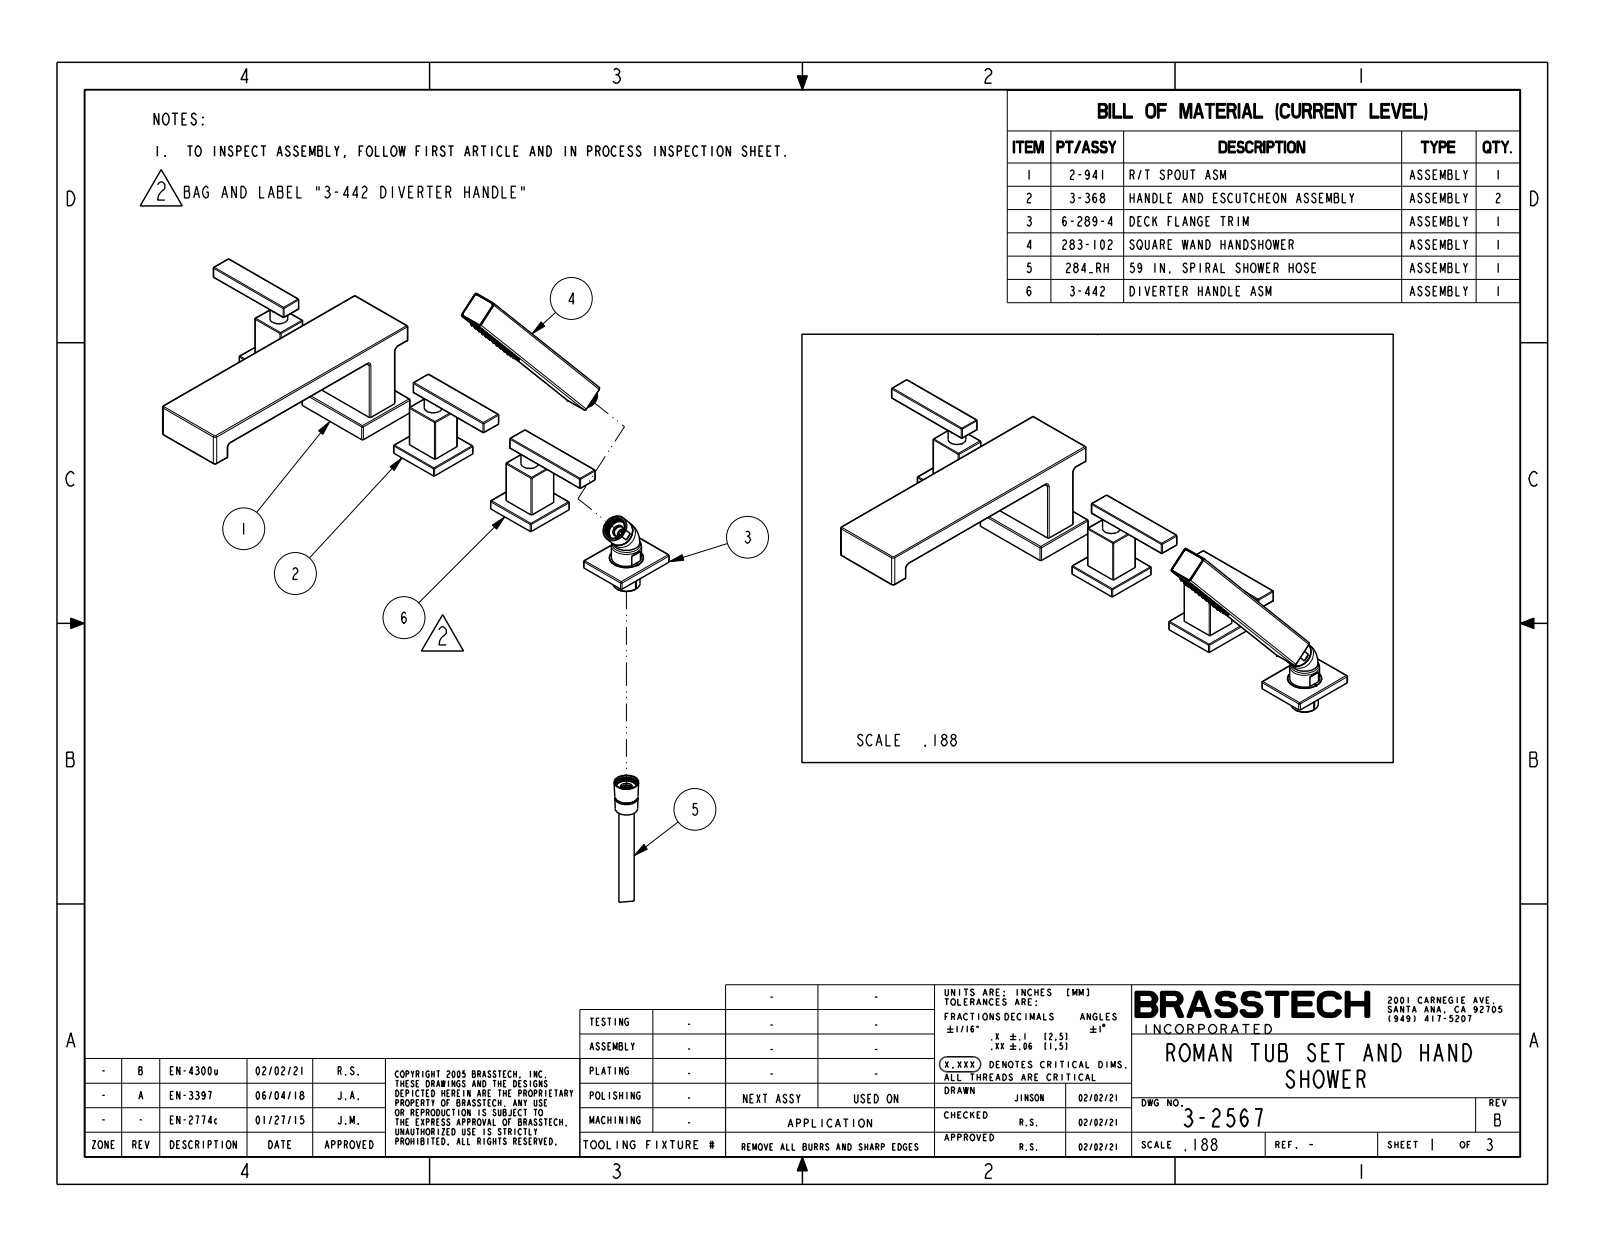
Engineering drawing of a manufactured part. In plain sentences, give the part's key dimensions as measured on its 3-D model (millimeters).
The part is named "3-2567". Its 3-D file was written by "CREO PARAMETRIC BY PTC INC, 2018400 (CONFIG_CONTROL_DESIGN)". It is 5 solids with 1086 faces: 150 planar, 312 cylindrical and 624 other. Overall it measures 558.4 by 254 by 222.8 millimeters. Its volume is 1 007 000 cubic millimeters and its surface area 164 000 square millimeters. Round holes: 44 of diameter 3.6, 1 of diameter 21.2. Round bosses or shafts: 3 of diameter 16.5, 3 of diameter 13.3, 1 of diameter 27.8, 1 of diameter 24.9, 1 of diameter 24.8, 1 of diameter 21. Partial cylindrical surfaces (rounded edges, fillets, slot ends): 70 of radius 0.8, 35 of radius 1, 16 of radius 0.3, 6 of radius 1.3, 4 of radius 1.7, 3 of radius 4.1, 2 of radius 2, 2 of radius 12.7. The main face-to-face distances are 95.5, 78.5, 17, 29.5, 1.8, 31.2, 1, 69.6, 6.4, 70.1. The hole center spacings are 8.5, 4.3, 11.4, 17.1, 15.3, 7.4, 22.1, 22.5.
